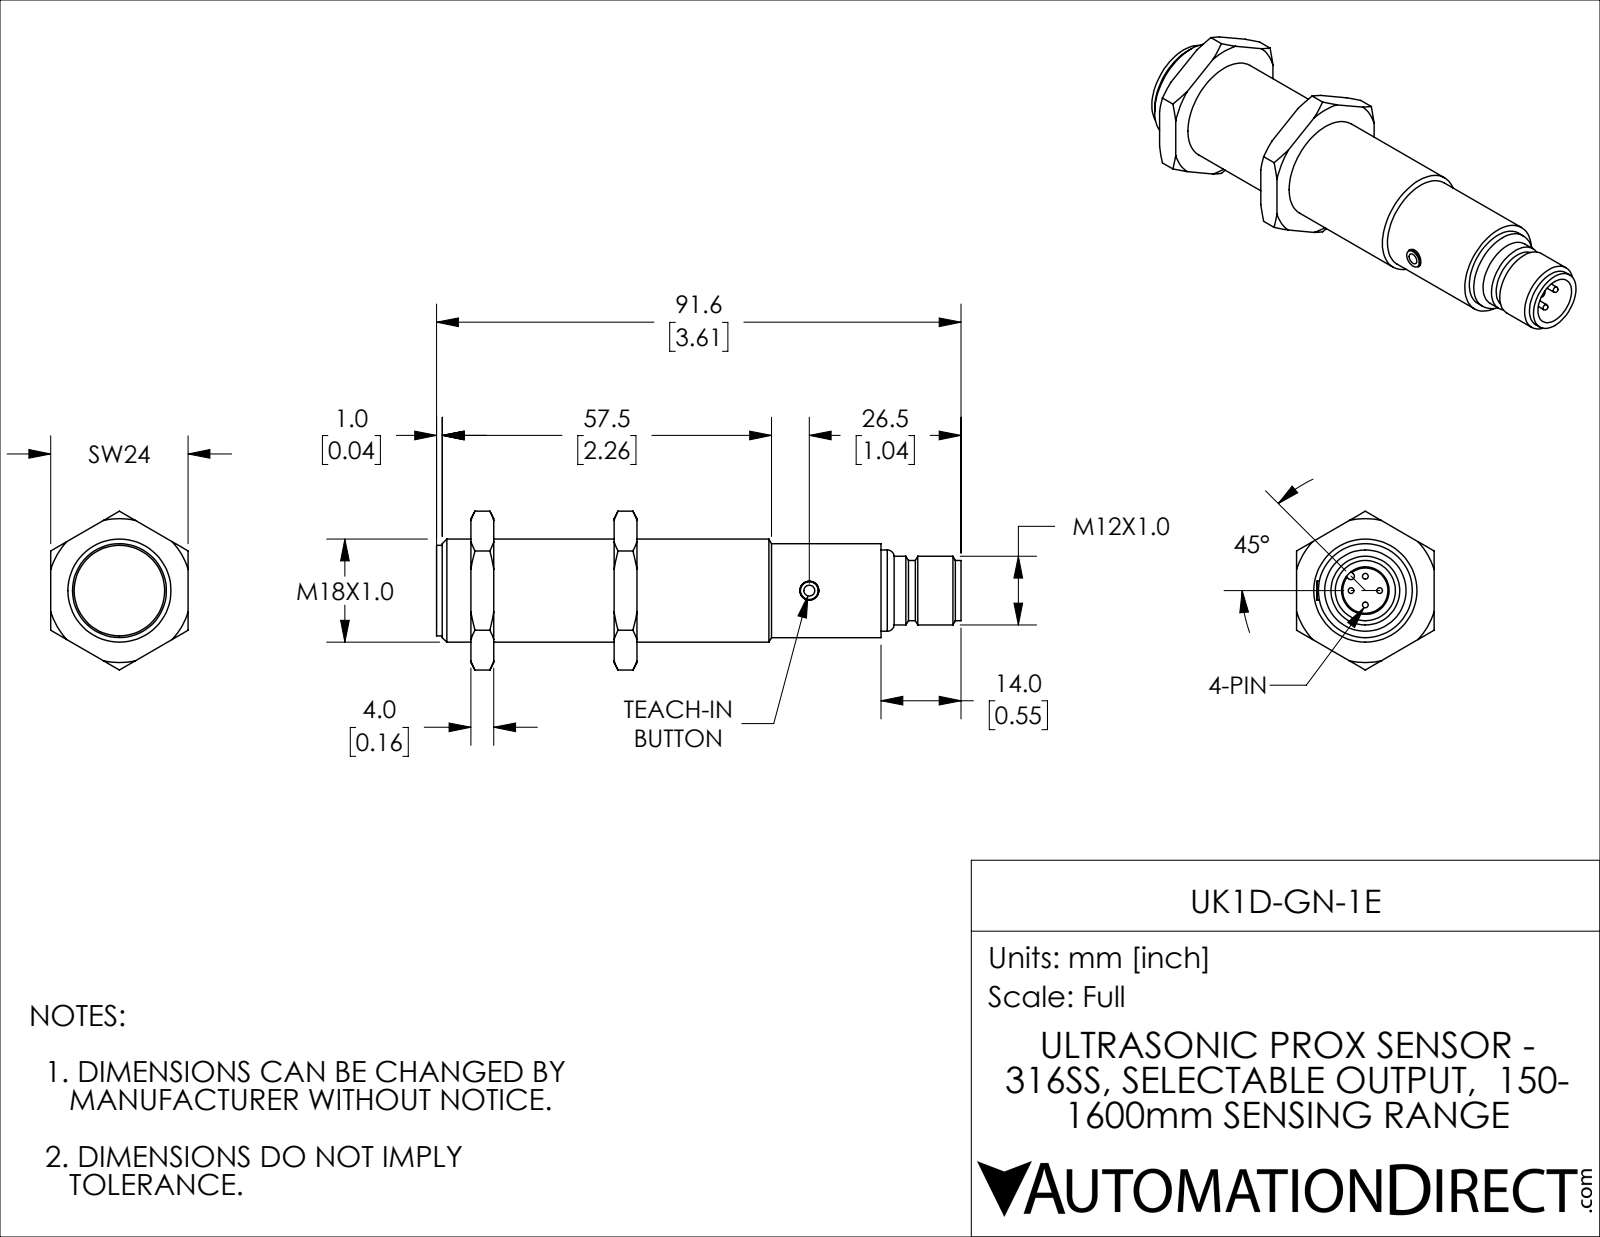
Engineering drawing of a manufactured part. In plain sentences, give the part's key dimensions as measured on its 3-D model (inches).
The part is named "UK1D-GN-1E". Its 3-D file was written by "SolidWorks 2018 (AUTOMOTIVE_DESIGN)". It is 4 solids with 113 faces: 27 planar, 35 cylindrical and 51 other. Overall it measures 3.606 by 1.091 by 0.945 inches. Its volume is 1.338 cubic inches and its surface area 11.97 square inches. Round holes: 1 of diameter 0.13, 1 of diameter 0.327, 1 of diameter 0.709. Round bosses or shafts: 4 of diameter 0.039, 1 of diameter 0.646, 1 of diameter 0.622, 1 of diameter 0.559, 1 of diameter 0.472, 1 of diameter 0.413. Partial cylindrical surfaces (rounded edges, fillets, slot ends): 1 of radius 0.024. The main face-to-face distances are 0.984, 0.157, 0.945, 1.142, 0.827, 0.236, 0.394, 1.22, 1.378, 3.055.
